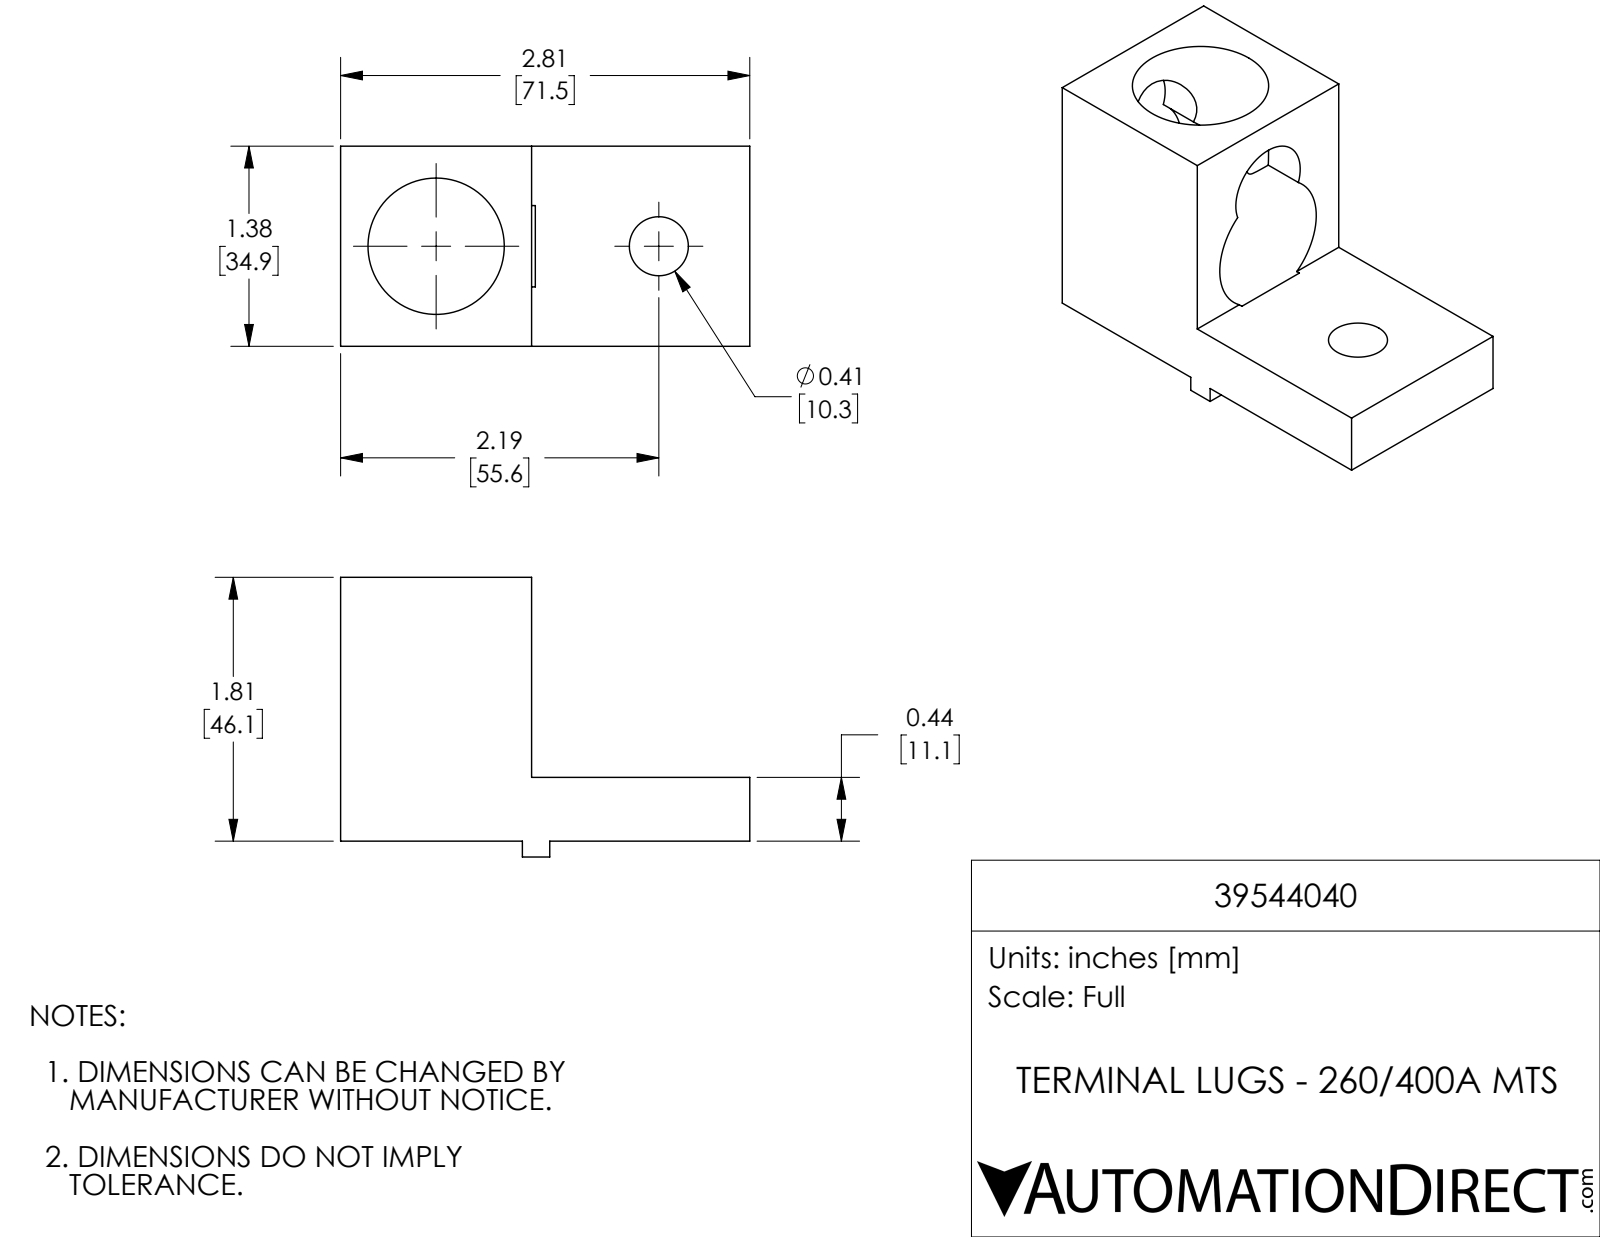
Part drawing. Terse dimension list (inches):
name: 39544040
written by: SolidWorks 2017 (AUTOMOTIVE_DESIGN)
unit: in
bodies: 1 solid, 22 faces (13 planar, 9 cylindrical, 0 other)
size: 2.813 × 1.922 × 1.375
volume: 2.749 in³; area: 22.08 in²
holes: 1× ⌀0.406, 1× ⌀0.937
rounds: 1× R0.313, 1× R0.469
face distances: 1.375, 0.438, 1.813, 1.375, 1.313, 2.813, 1.5, 0.109, 0.547, 1.922
hole spacings: 1.531
